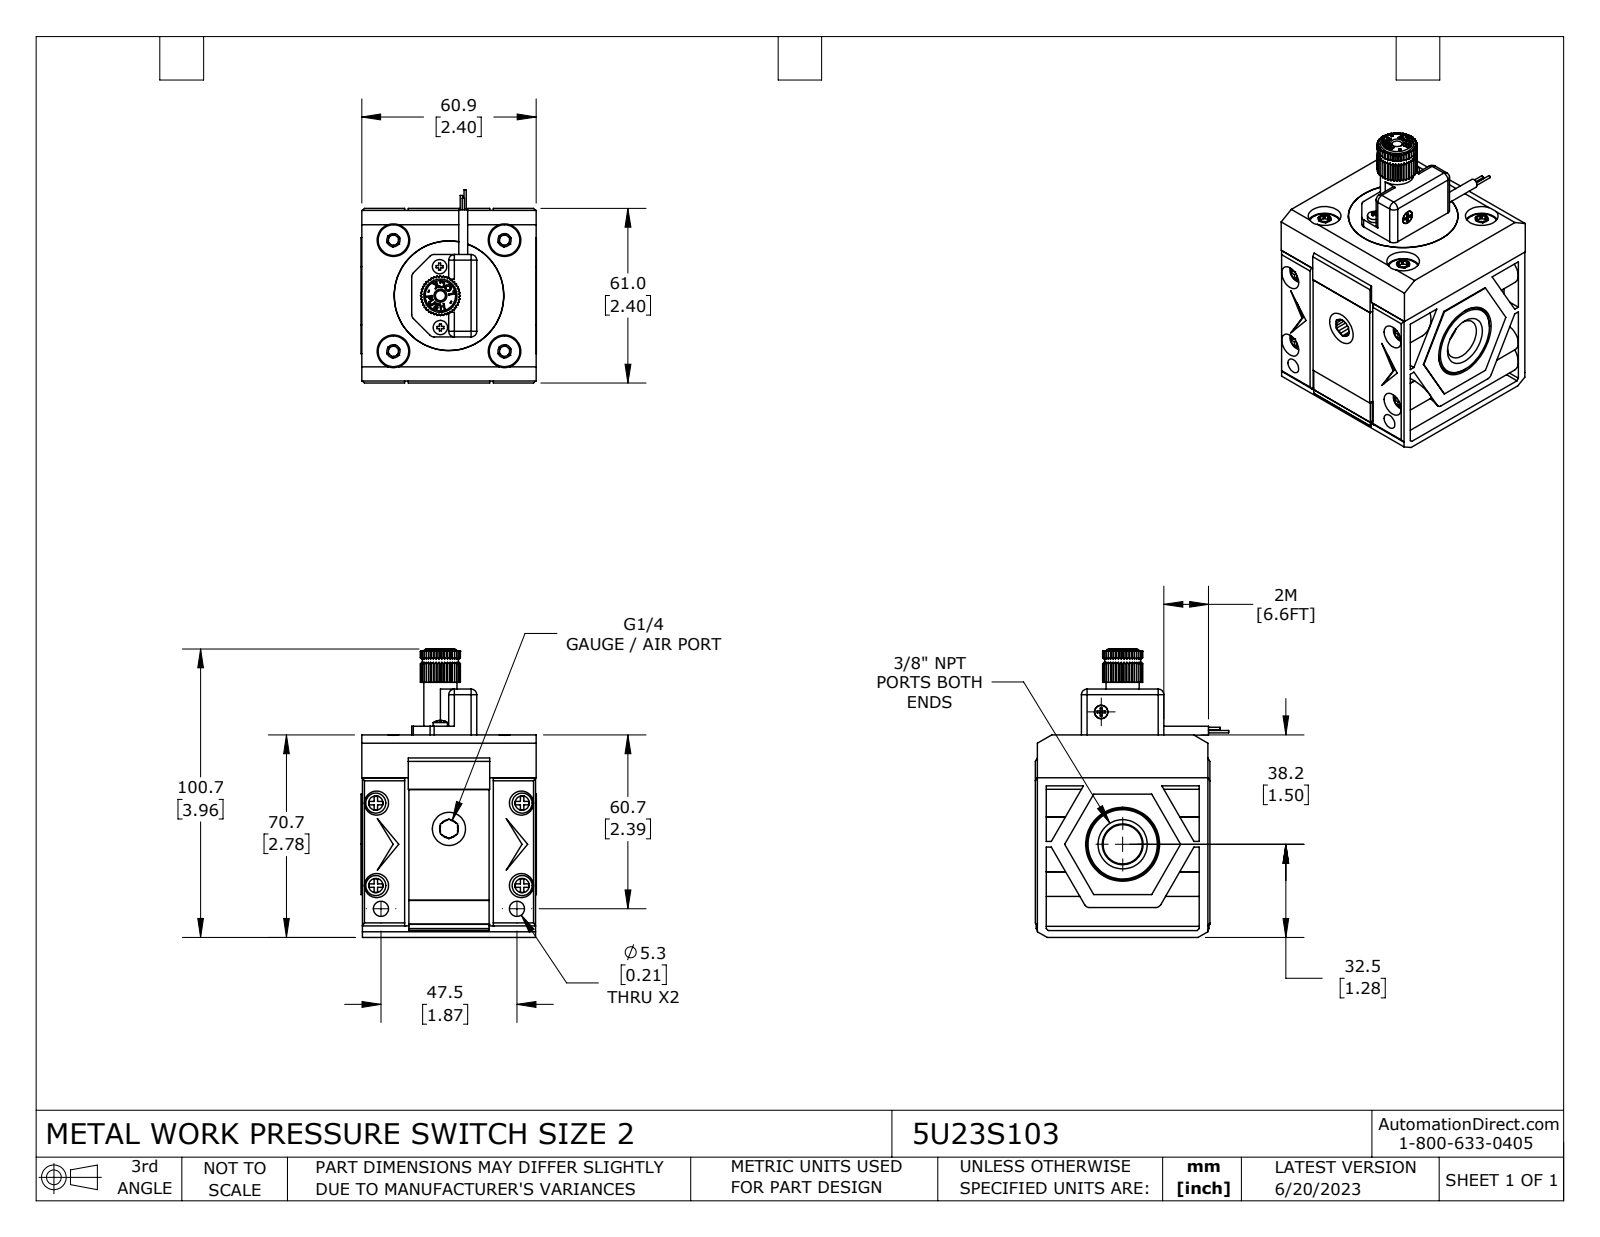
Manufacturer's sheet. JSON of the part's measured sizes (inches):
{"part_name": "5U23S103", "step_written_by": "SolidWorks 2021 (CONFIG_CONTROL_DESIGN)", "units": "inches", "bodies": {"solids": 13, "faces": 1217, "planar": 682, "cylindrical": 343, "other": 192}, "overall_size": [3.965, 2.657, 2.411], "volume_in3": 12.82, "surface_area_in2": 110.7, "round_holes": [[0.128, 4], [0.165, 4], [0.331, 4], [0.449, 4], [0.209, 2], [0.071, 1], [0.457, 1], [1.25, 1], [1.508, 1]], "round_bosses_or_shafts": [[0.276, 4], [0.189, 4], [0.15, 4], [0.031, 3], [0.197, 2], [1.504, 1], [1.248, 1], [1.035, 1]], "partial_cylinders_radius": [[0.011, 28], [0.079, 14], [0.069, 4], [0.191, 4], [0.242, 2], [0.008, 1], [0.009, 1], [0.009, 1]], "face_to_face_distances": [2.39, 0.094, 2.193, 2.098, 2.402, 0.028, 0.591, 1.799, 0.299, 2.783], "hole_center_spacings": [1.08, 1.528, 0.325, 1.057, 1.134, 1.265, 1.443, 1.454]}
